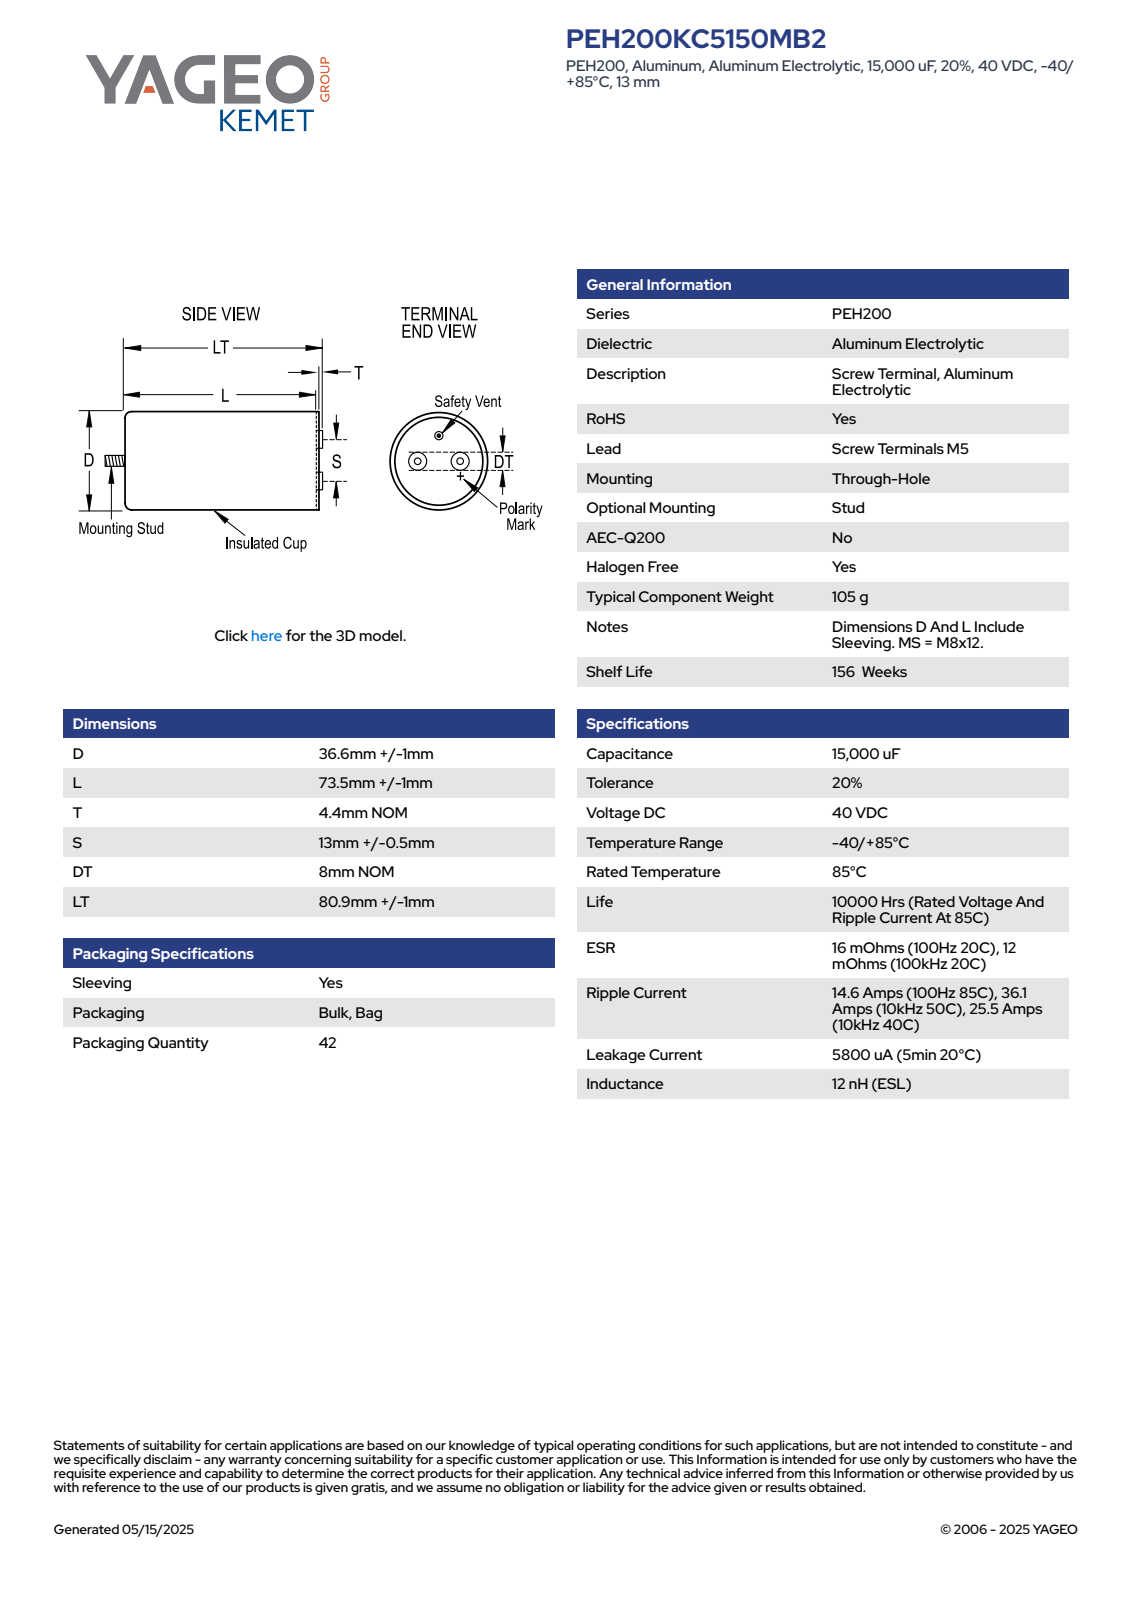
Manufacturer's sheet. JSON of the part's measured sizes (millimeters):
{"part_name": "CARCS_D37.6L74.5S13T4.4; Round_Terminal; Stud8; Can_Round_7", "step_written_by": "SolidWorks 2014 (AUTOMOTIVE_DESIGN)", "units": "millimeters", "bodies": {"solids": 4, "faces": 147, "planar": 54, "cylindrical": 61, "other": 32}, "overall_size": [93.9, 37.6, 37.6], "volume_mm3": 83727, "surface_area_mm2": 12712, "round_holes": [[5, 2], [35.6, 1]], "round_bosses_or_shafts": [[8, 3], [37.6, 1], [7.7, 1]], "partial_cylinders_radius": [[18.79, 1]], "face_to_face_distances": [74.5, 3, 77.5, 4.4, 7.4, 81.9, 1, 93.9, 89.5, 86.5], "hole_center_spacings": [6.5, 13]}
